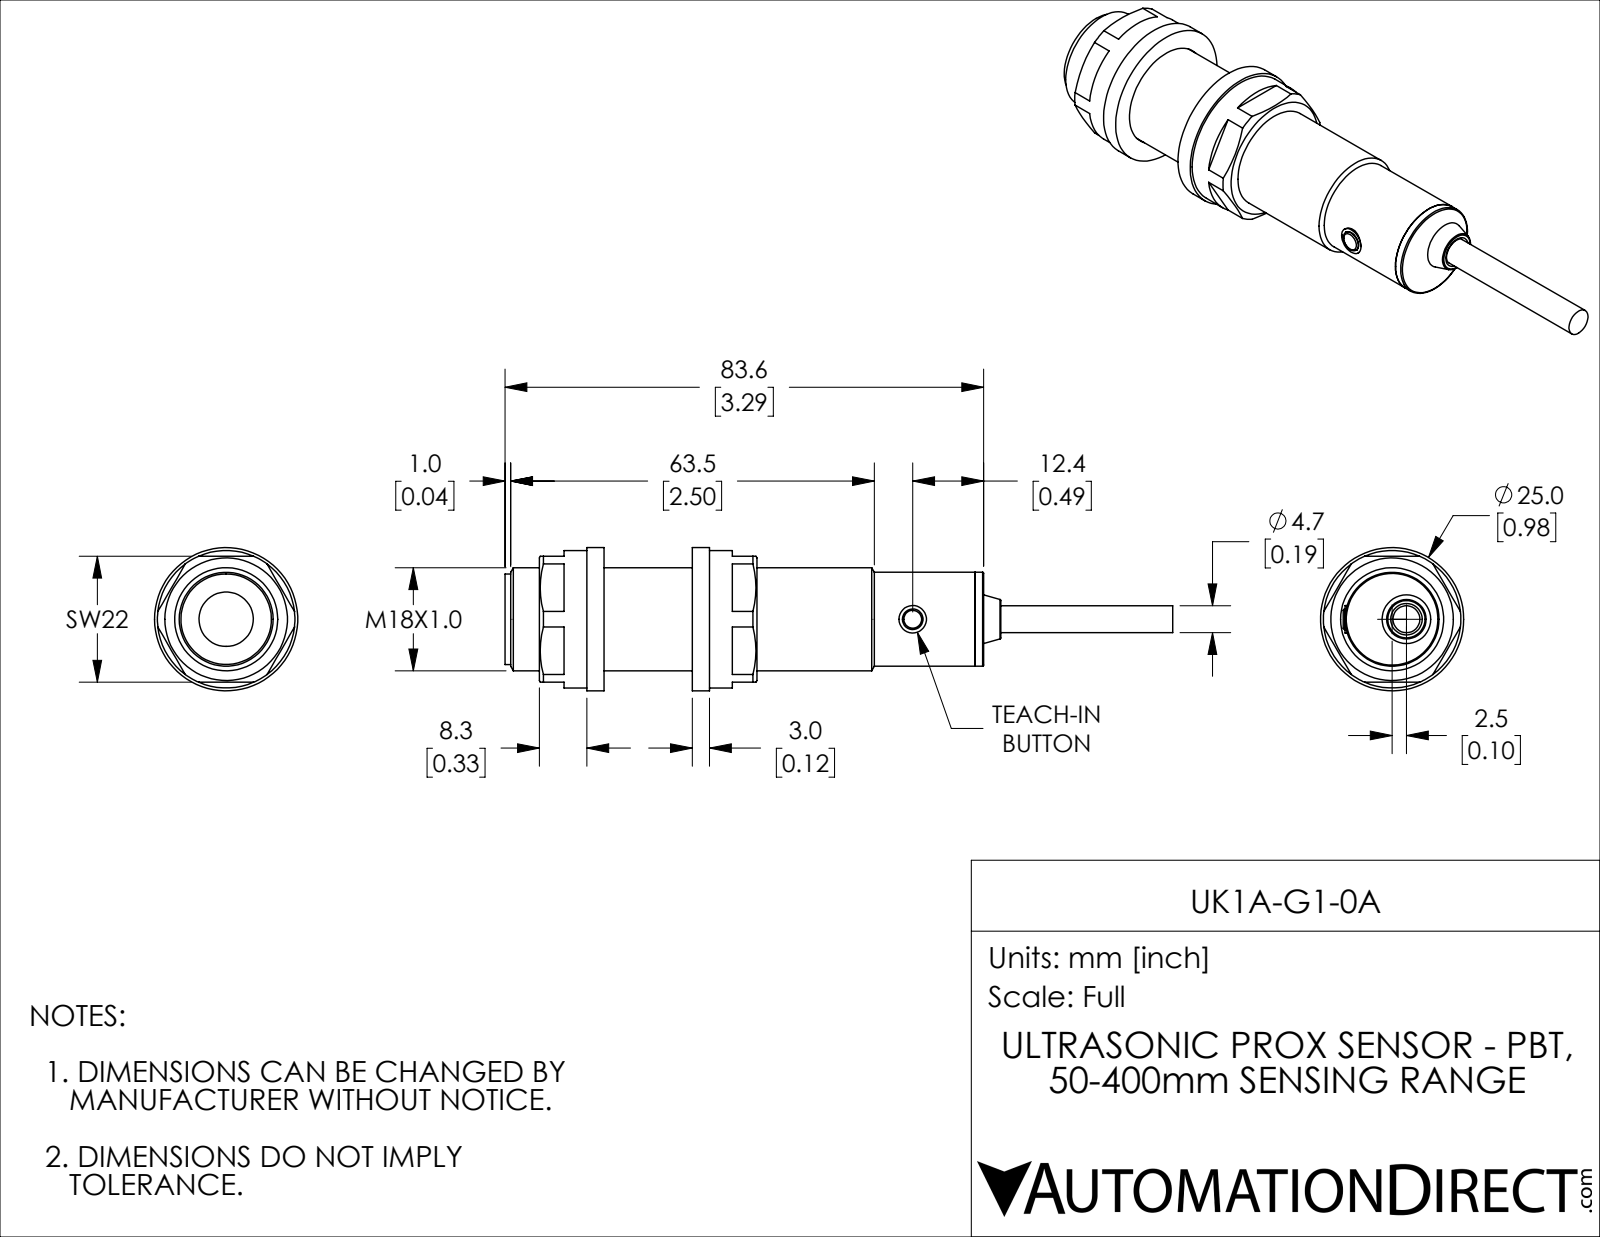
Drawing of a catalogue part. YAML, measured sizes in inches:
part_name: "UK1A-G1-0A"
step_written_by: "SolidWorks 2018 (AUTOMOTIVE_DESIGN)"
units: inches
bodies: {solids: 10, faces: 107, planar: 49, cylindrical: 40, other: 18}
overall_size: [4.591, 0.984, 0.984]
volume: 1.539
surface_area: 17.7
round_holes:
  - {diameter: 0.185, count: 2}
  - {diameter: 0.142, count: 1}
  - {diameter: 0.374, count: 1}
  - {diameter: 0.709, count: 1}
  - {diameter: 0.717, count: 1}
round_bosses_or_shafts:
  - {diameter: 0.984, count: 1}
  - {diameter: 0.945, count: 1}
  - {diameter: 0.646, count: 1}
  - {diameter: 0.622, count: 1}
  - {diameter: 0.213, count: 1}
  - {diameter: 0.189, count: 1}
face_to_face_distances: [0.118, 0.724, 0.843, 2.669, 1.827, 0.524, 1.366, 3.193, 0.642, 2.551]
hole_center_spacings: [0.098]
